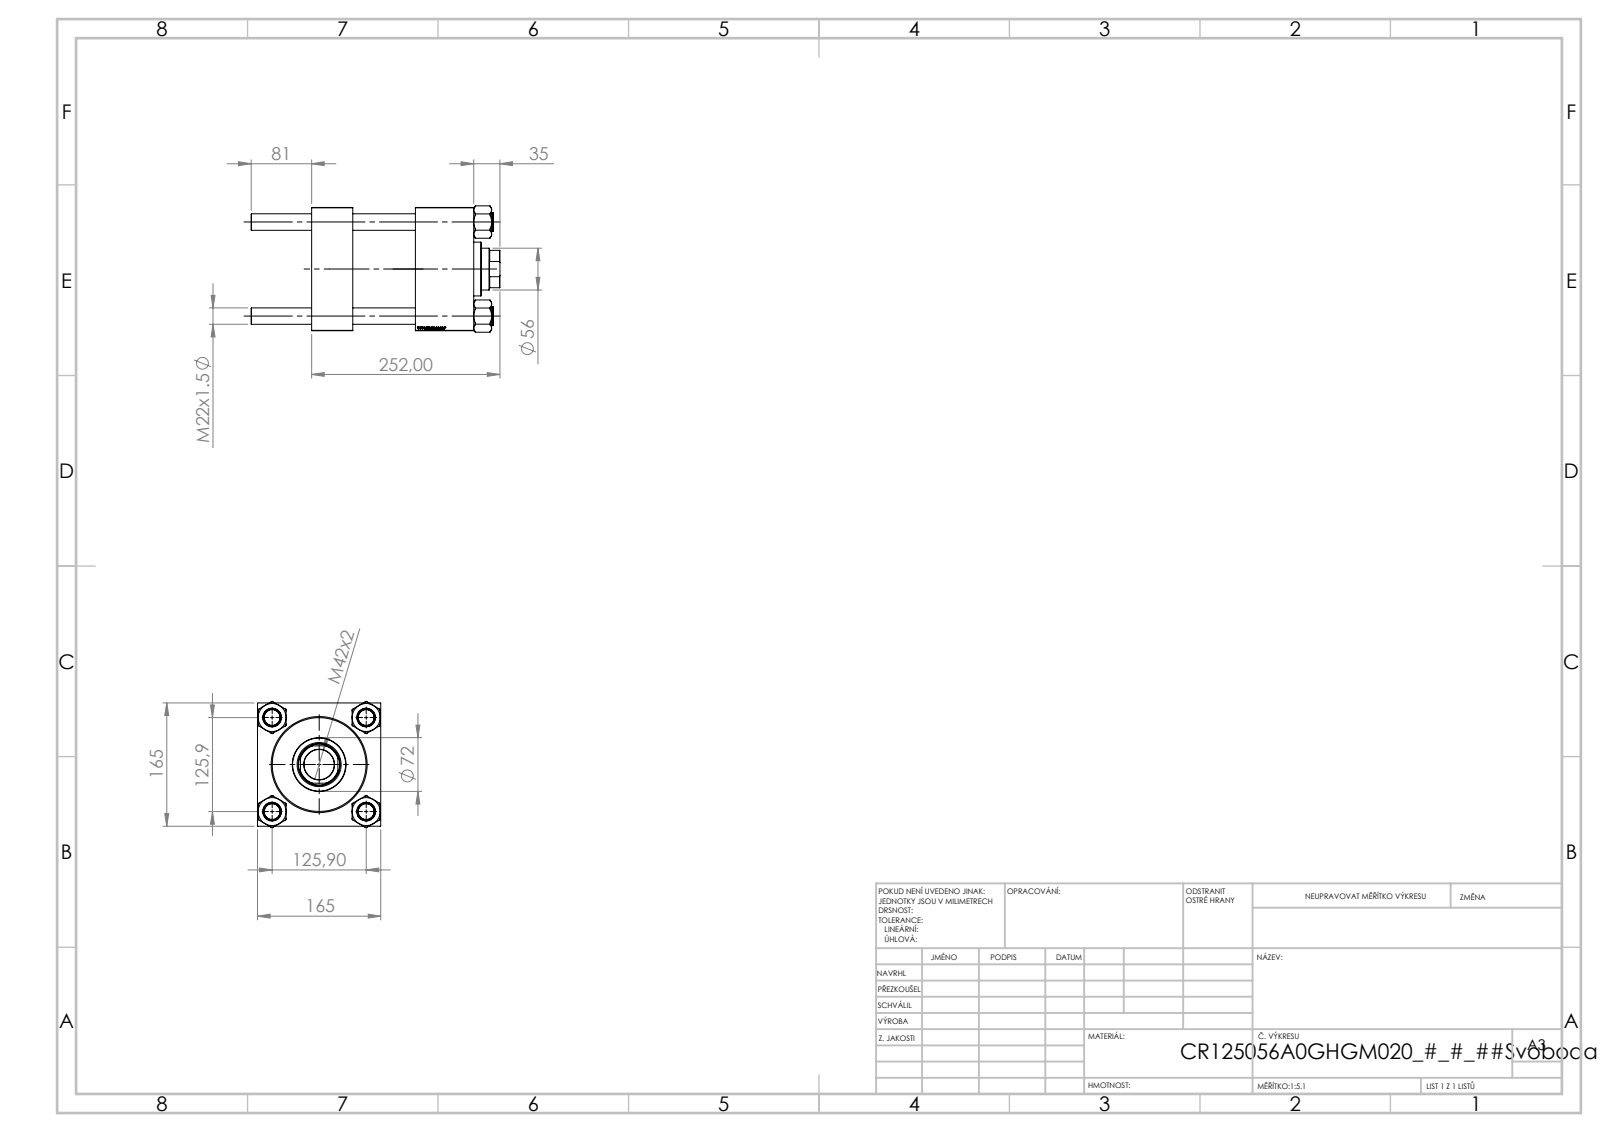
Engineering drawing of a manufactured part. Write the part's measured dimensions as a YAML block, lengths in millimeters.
part_name: "NUT_M5; V215CR_BODY_A; V215CR_VCP; CR025_012_A_0_G_A_G_M_020_+#_##_TYCINKA (+1 more)"
step_written_by: "SolidWorks 2019 (CONFIG_CONTROL_DESIGN)"
units: millimeters
bodies: {solids: 11, faces: 1182, planar: 568, cylindrical: 78, other: 536}
overall_size: [333, 169.14, 165]
volume: 4680000
surface_area: 548648
round_holes:
  - {diameter: 22, count: 4}
  - {diameter: 7, count: 2}
  - {diameter: 32.24, count: 2}
  - {diameter: 45, count: 2}
  - {diameter: 40.5, count: 1}
  - {diameter: 56, count: 1}
  - {diameter: 59, count: 1}
  - {diameter: 96, count: 1}
  - {diameter: 125, count: 1}
  - {diameter: 125.5, count: 1}
round_bosses_or_shafts:
  - {diameter: 25, count: 4}
  - {diameter: 131, count: 1}
  - {diameter: 72, count: 1}
partial_cylinders:
  - {radius: 27, count: 1}
face_to_face_distances: [165, 55, 162, 217, 139, 84, 78, 188.3, 133.3, 49.3]
hole_center_spacings: [89.02, 125.9, 178.05, 138.5]
